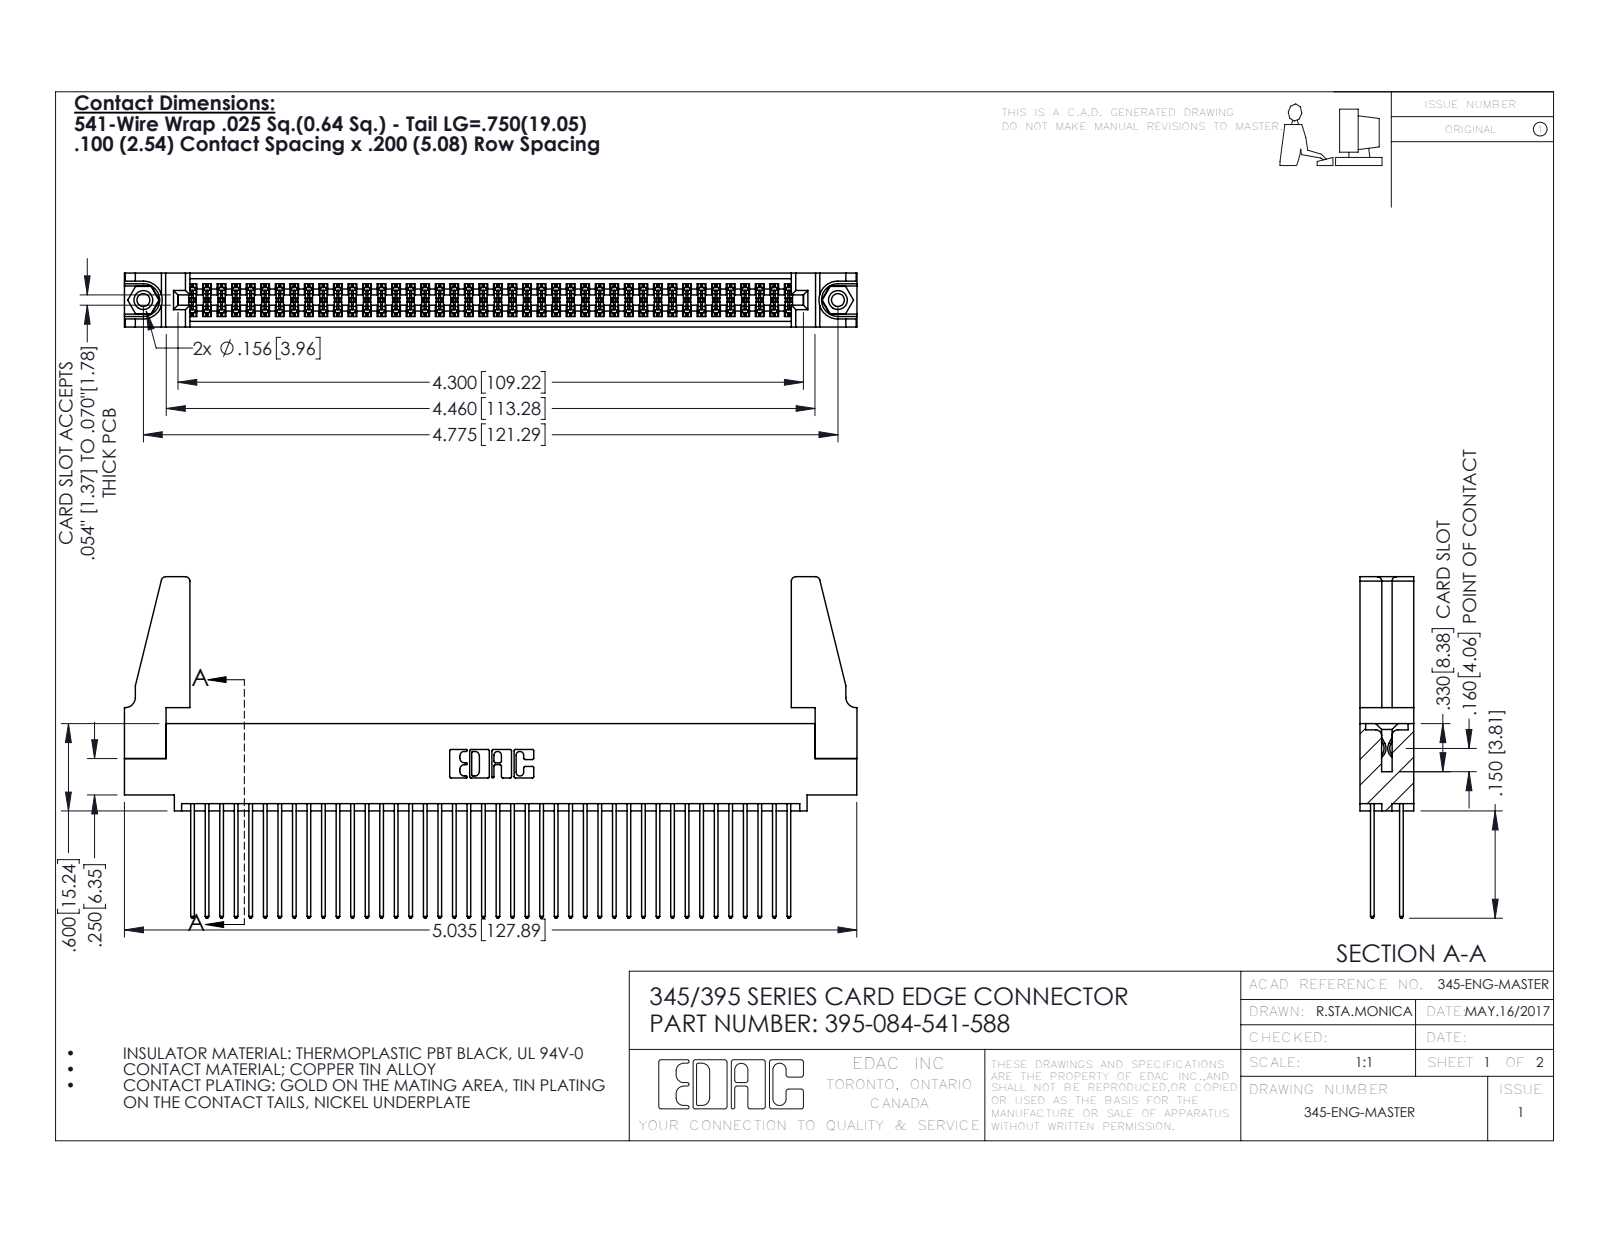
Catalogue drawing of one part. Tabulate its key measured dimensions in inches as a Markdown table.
| quantity | value |
| --- | --- |
| part name | 345 Part_0.110 Offset - 0.156 Dia-TH; 345-220-078_345-220-088; 395-084-541-588; 345-292-001_345-293-141 (+1 more) |
| STEP written by | SolidWorks 2016 (CONFIG_CONTROL_DESIGN) |
| units | inches |
| bodies | 89 solids, 4454 faces (2928 planar, 1510 cylindrical, 16 other) |
| overall size | 5.036 × 2.347 × 0.37 |
| volume | 0.982 in³ |
| surface area | 37.9 in² |
| round holes (diameter × count) | 0.089 × 2, 0.125 × 2, 0.156 × 2, 0.064 × 1 |
| round bosses / shafts (diameter × count) | 0.155 × 2 |
| partial cylindrical surfaces (radius × count) | 0.006 × 126, 0.01 × 84, 0.01 × 22, 0.03 × 8, 0.007 × 6, 0.031 × 6, 0.026 × 3, 0.014 × 2 |
| main face-to-face distances | 0.072, 0.298, 0.2, 0.098, 0.272, 0.025, 0.37, 0.225, 0.175, 0.149 |
| hole center spacings | 0.27, 4.539, 4.775 |
